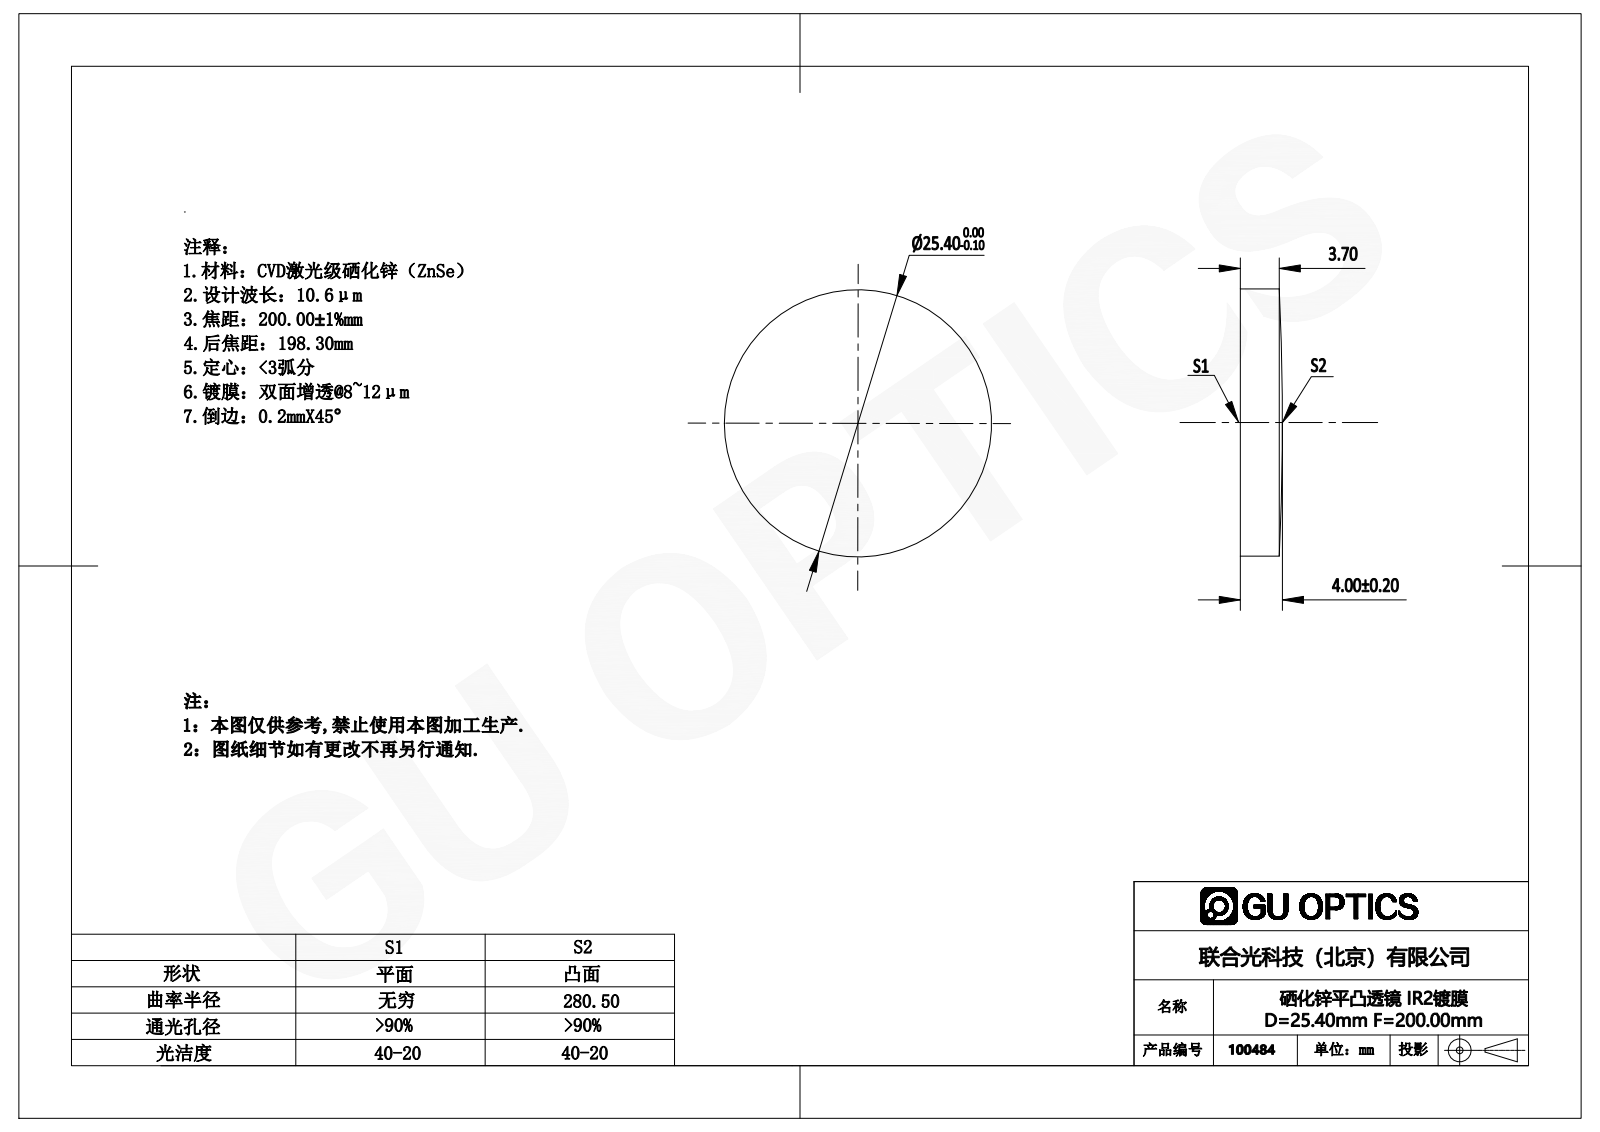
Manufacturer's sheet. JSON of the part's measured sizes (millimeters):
{"part_name": "100472", "step_written_by": "SolidWorks 2016 (AUTOMOTIVE_DESIGN)", "units": "millimeters", "bodies": {"solids": 1, "faces": 5, "planar": 1, "cylindrical": 2, "other": 2}, "overall_size": [25.4, 25.4, 4], "volume_mm3": 1951, "surface_area_mm2": 1309, "round_bosses_or_shafts": [[25.4, 1]]}
